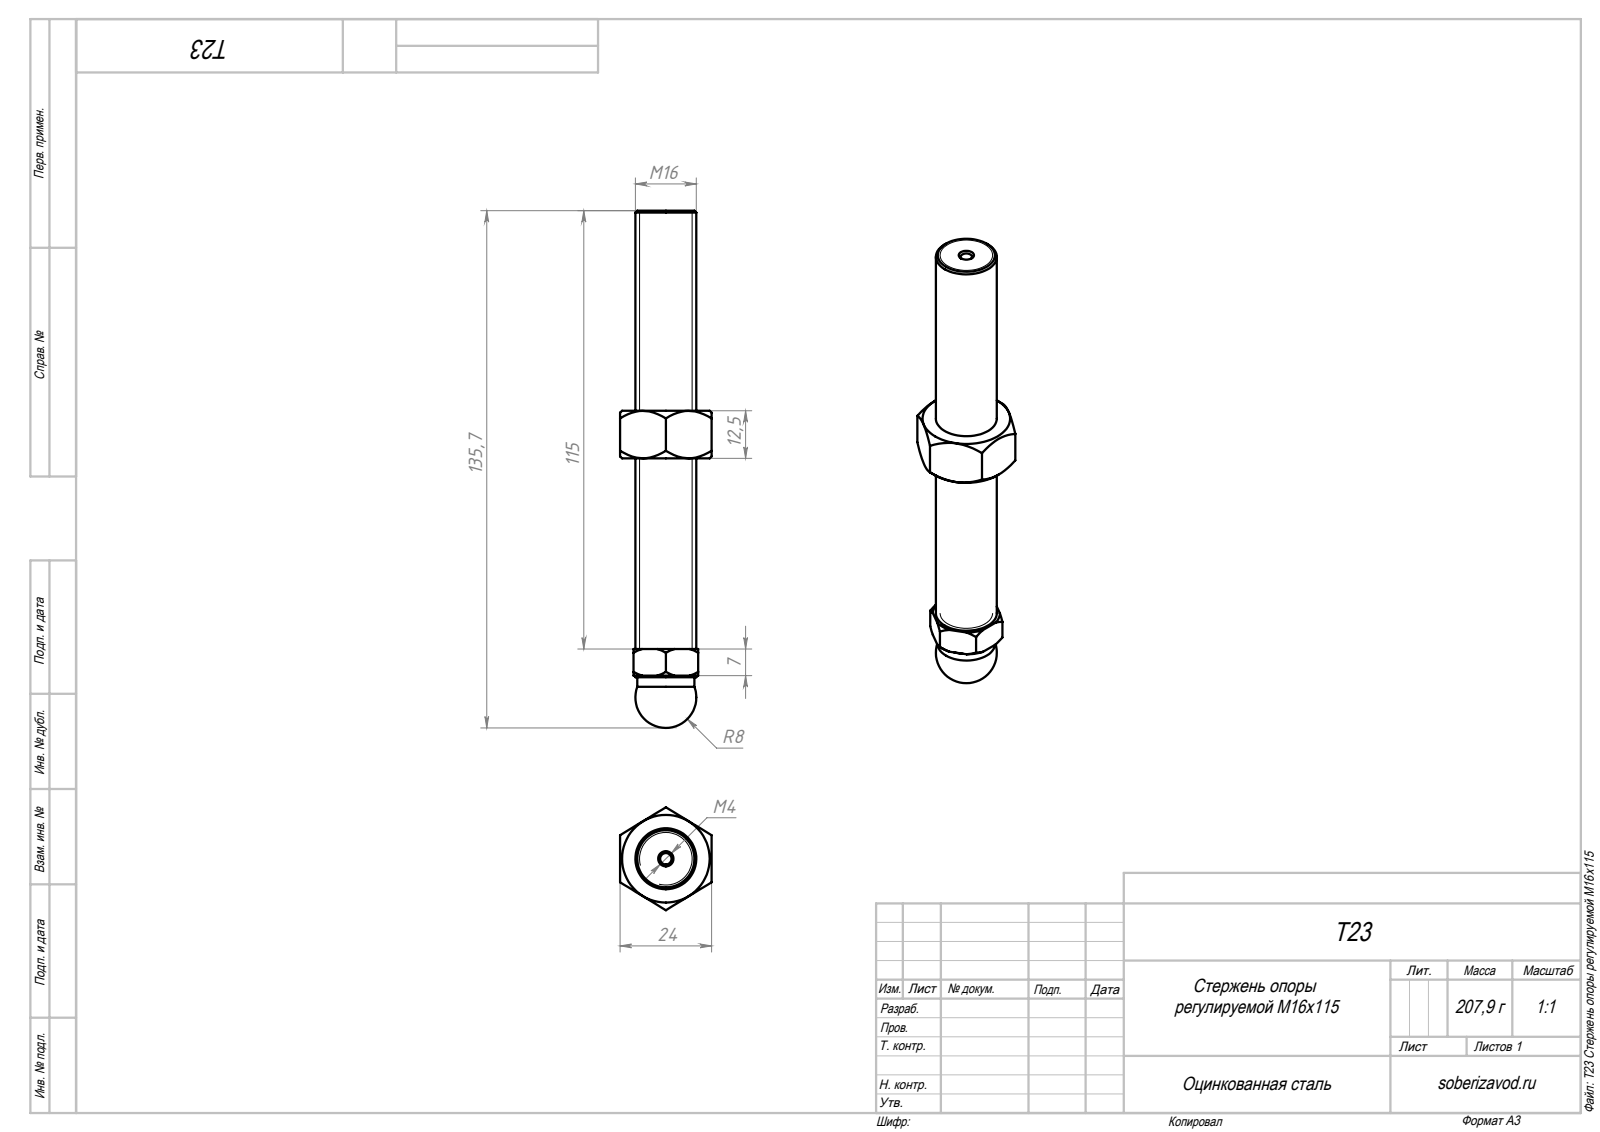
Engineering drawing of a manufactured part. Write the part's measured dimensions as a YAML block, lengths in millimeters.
part_name: "T23 Стержень опоры регулируемой М16х115"
step_written_by: "SolidWorks 2018 (AUTOMOTIVE_DESIGN)"
units: millimeters
bodies: {solids: 1, faces: 59, planar: 21, cylindrical: 8, other: 30}
overall_size: [135.72, 27, 24]
volume: 30286
surface_area: 8060
round_holes:
  - {diameter: 3, count: 1}
round_bosses_or_shafts:
  - {diameter: 16, count: 1}
  - {diameter: 15, count: 1}
face_to_face_distances: [23.06, 12.5, 17, 65, 52.5, 24, 3.5, 20.5, 50, 62.5]
